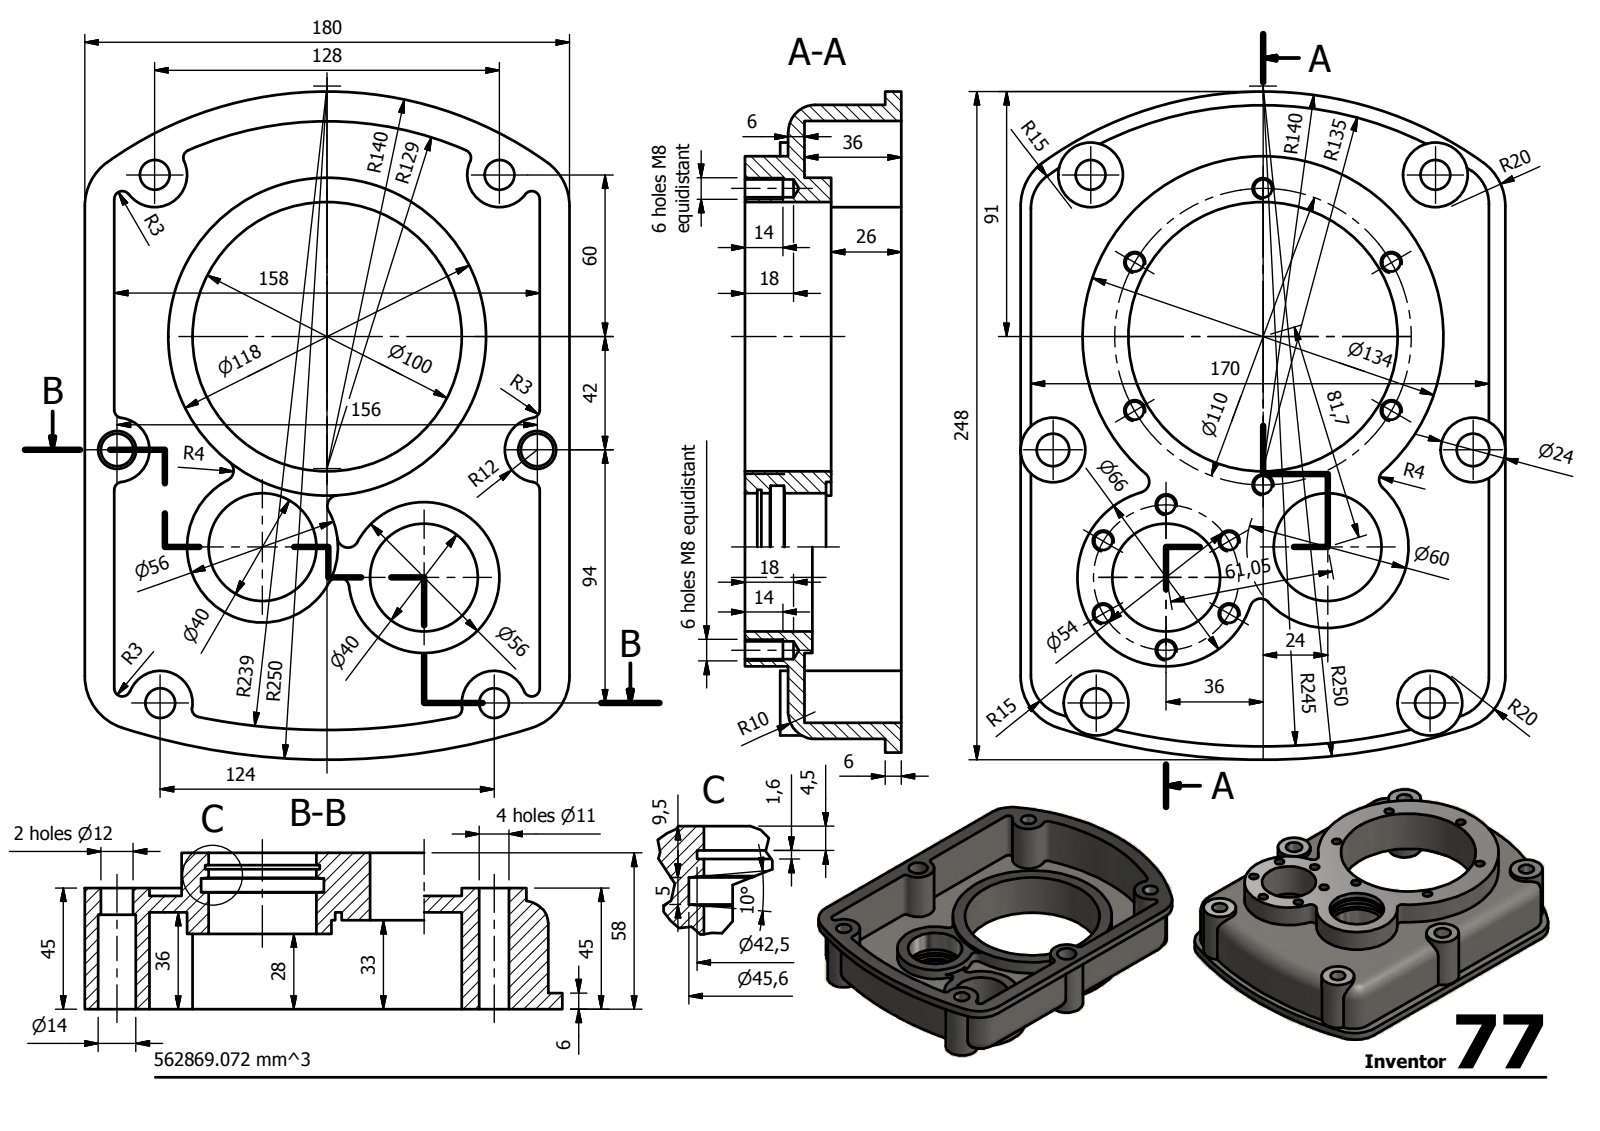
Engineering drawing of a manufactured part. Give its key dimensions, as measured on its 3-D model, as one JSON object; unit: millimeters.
{"step_written_by": "Autodesk Inventor 2014 (AUTOMOTIVE_DESIGN)", "units": "millimeters", "bodies": {"solids": 1, "faces": 140, "planar": 29, "cylindrical": 86, "other": 25}, "overall_size": [248, 180, 58], "volume_mm3": 562866, "surface_area_mm2": 167190, "round_holes": [[6.65, 12], [11, 4], [12, 2], [14, 2], [40, 2], [42.5, 1], [45.6, 1], [100, 1]], "round_bosses_or_shafts": [[24, 6], [118, 1], [56, 1]], "partial_cylinders_radius": [[3, 12], [4, 7], [15, 4], [20, 4], [10, 2], [28, 1], [30, 1], [33, 1]], "face_to_face_distances": [6, 36, 16, 22, 42, 58, 158, 30, 7.14, 165.14], "hole_center_spacings": [27, 55, 46.76, 95.26, 54, 110, 33.65, 36.39]}
